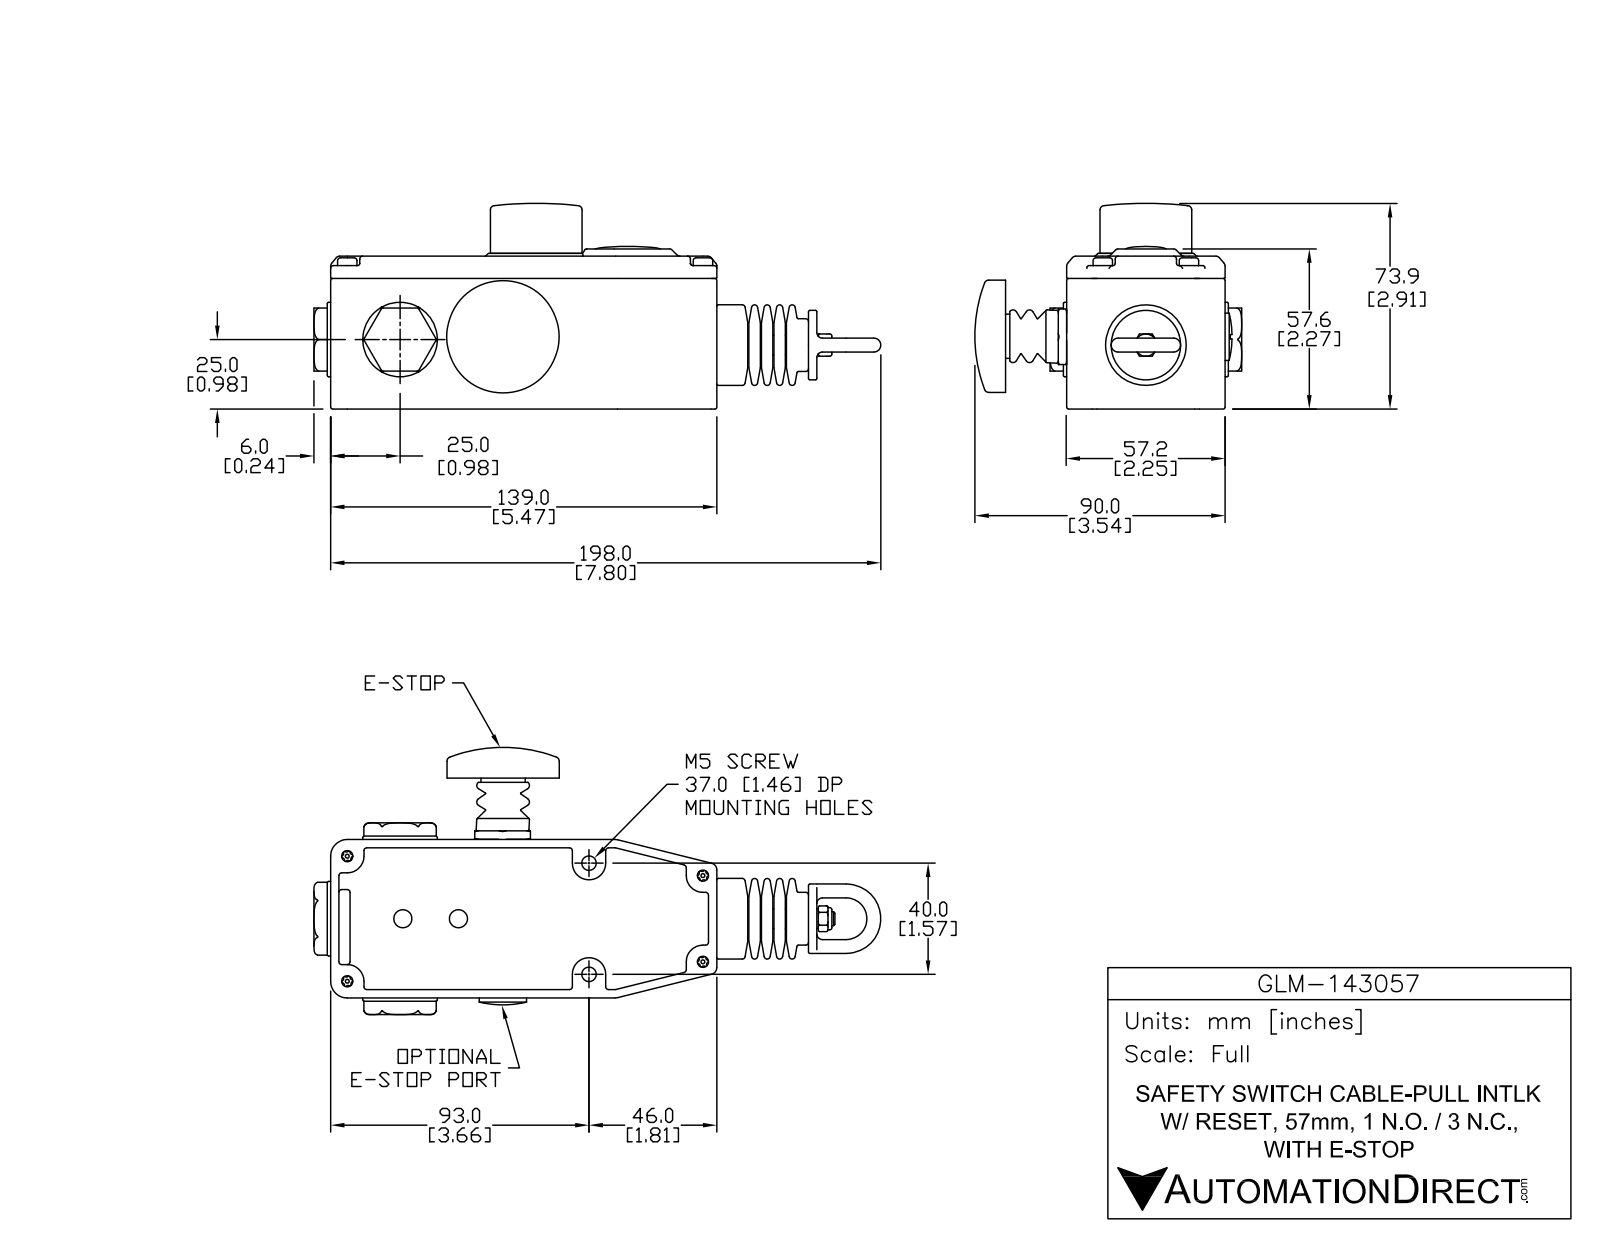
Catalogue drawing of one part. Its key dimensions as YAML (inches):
part_name: "GLM-143057"
step_written_by: "SolidWorks 2013 (AUTOMOTIVE_DESIGN)"
units: inches
bodies: {solids: 1, faces: 451, planar: 134, cylindrical: 154, other: 163}
overall_size: [8.031, 3.799, 2.909]
volume: 28.45
surface_area: 87.45
round_holes:
  - {diameter: 0.157, count: 4}
  - {diameter: 0.205, count: 2}
  - {diameter: 1.339, count: 1}
round_bosses_or_shafts:
  - {diameter: 0.276, count: 5}
  - {diameter: 1.055, count: 2}
  - {diameter: 0.197, count: 2}
  - {diameter: 1.575, count: 1}
  - {diameter: 1.386, count: 1}
  - {diameter: 1.299, count: 1}
  - {diameter: 1.142, count: 1}
  - {diameter: 0.984, count: 1}
partial_cylinders:
  - {radius: 0.02, count: 30}
  - {radius: 0.006, count: 19}
  - {radius: 0.01, count: 12}
  - {radius: 0.039, count: 8}
  - {radius: 0.177, count: 2}
  - {radius: 0.18, count: 2}
  - {radius: 0.276, count: 2}
  - {radius: 0.512, count: 2}
face_to_face_distances: [2.153, 2.252, 2.165, 0.013, 5.472, 0.248, 2.5, 3.417, 1.165, 0.744]
hole_center_spacings: [1.22, 1.575, 1.624, 1.624, 1.772, 2.134, 2.136, 3.426]
